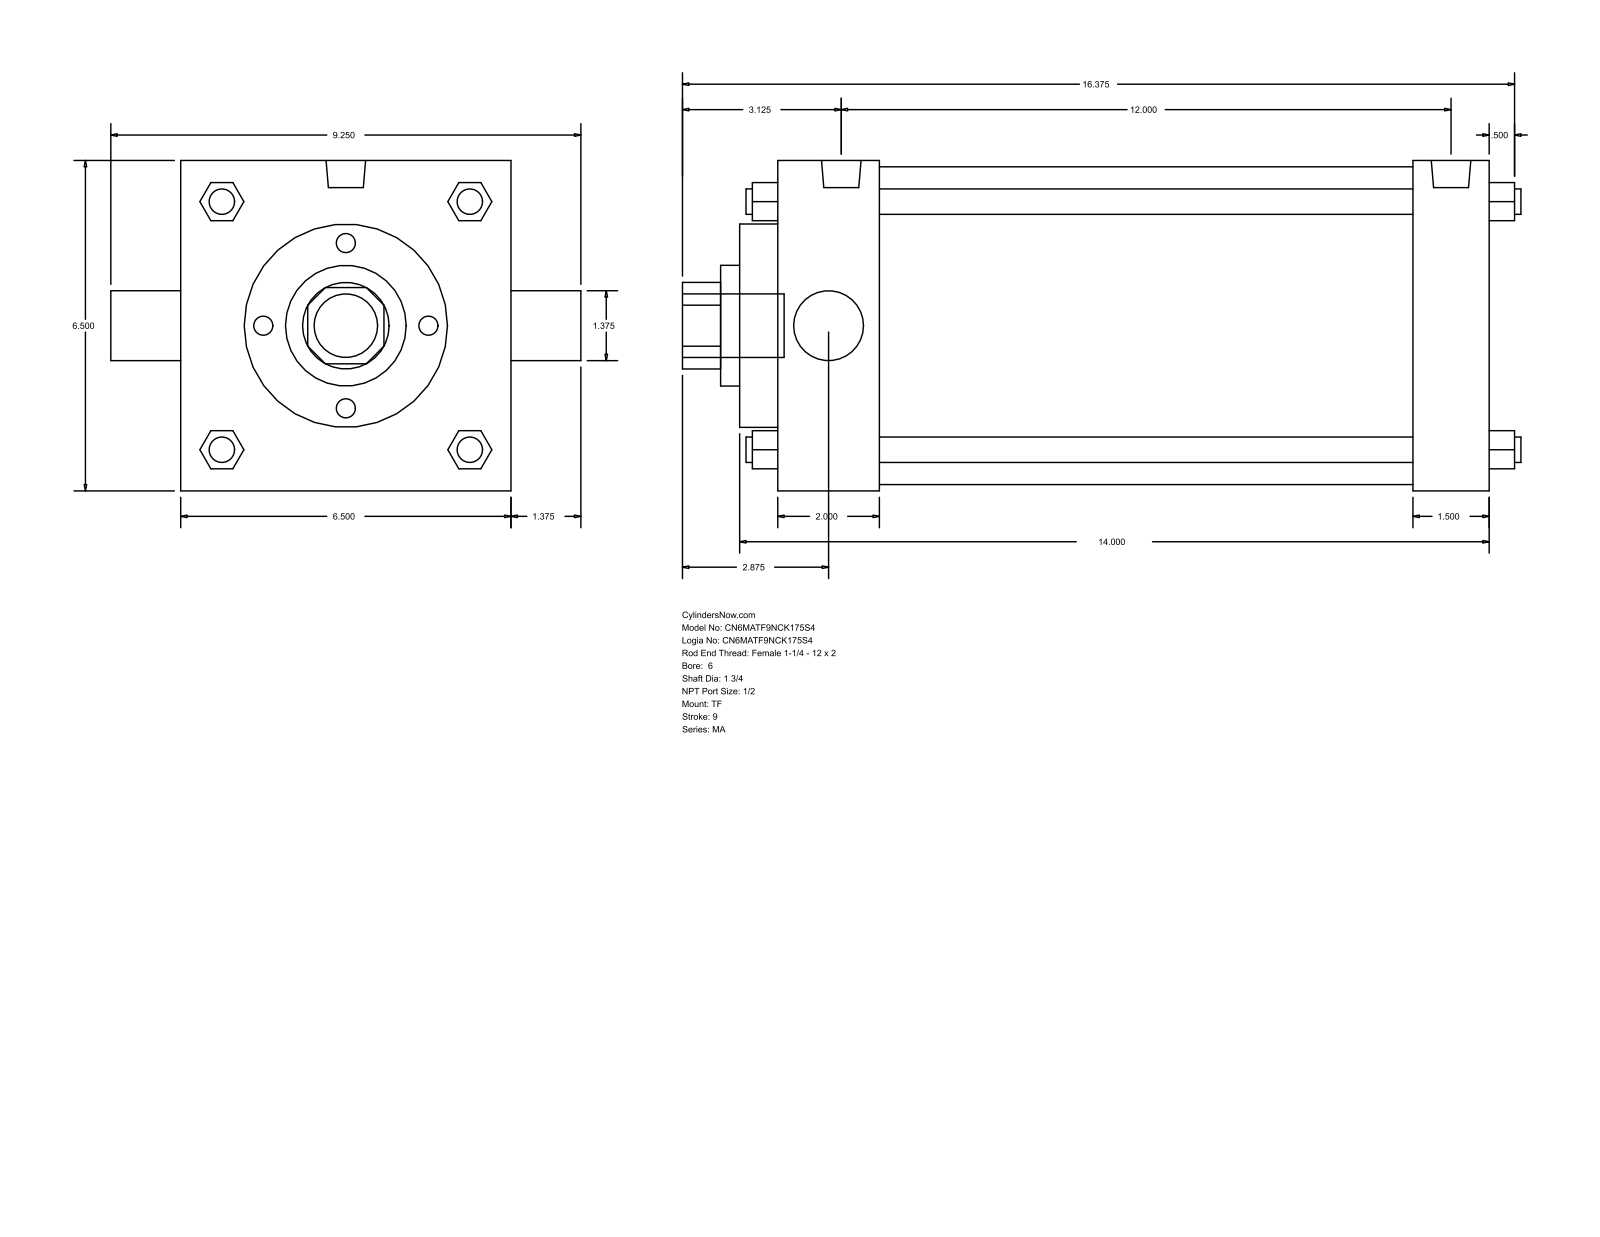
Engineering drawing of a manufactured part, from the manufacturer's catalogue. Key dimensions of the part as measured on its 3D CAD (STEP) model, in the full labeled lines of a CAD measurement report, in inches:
Part name (STEP PRODUCT): MA_TF__0600_1.75
STEP written by: GSSL Pune (CONFIG_CONTROL_DESIGN)
Units: inches
Bodies: 0 solids, 122 faces (93 planar, 29 cylindrical, 0 other)
Overall size (bounding box): 16.5 × 9.25 × 6.5
Round holes (diameter × count): ⌀1.375 ×1, ⌀1.75 ×1, ⌀2.375 ×1, ⌀4 ×1, ⌀6.25 ×1
Round bosses / shafts (diameter × count): ⌀0.5 ×4, ⌀0.687 ×3, ⌀0.778 ×2, ⌀1.25 ×1
Partial cylindrical surfaces — rounded edges, fillets, slot ends (radius × count): R0.852 ×1
Main face-to-face distances: 6.5, 14, 0.75, 2, 12, 12.5, 10.5, 1.5, 2.75, 13.25
